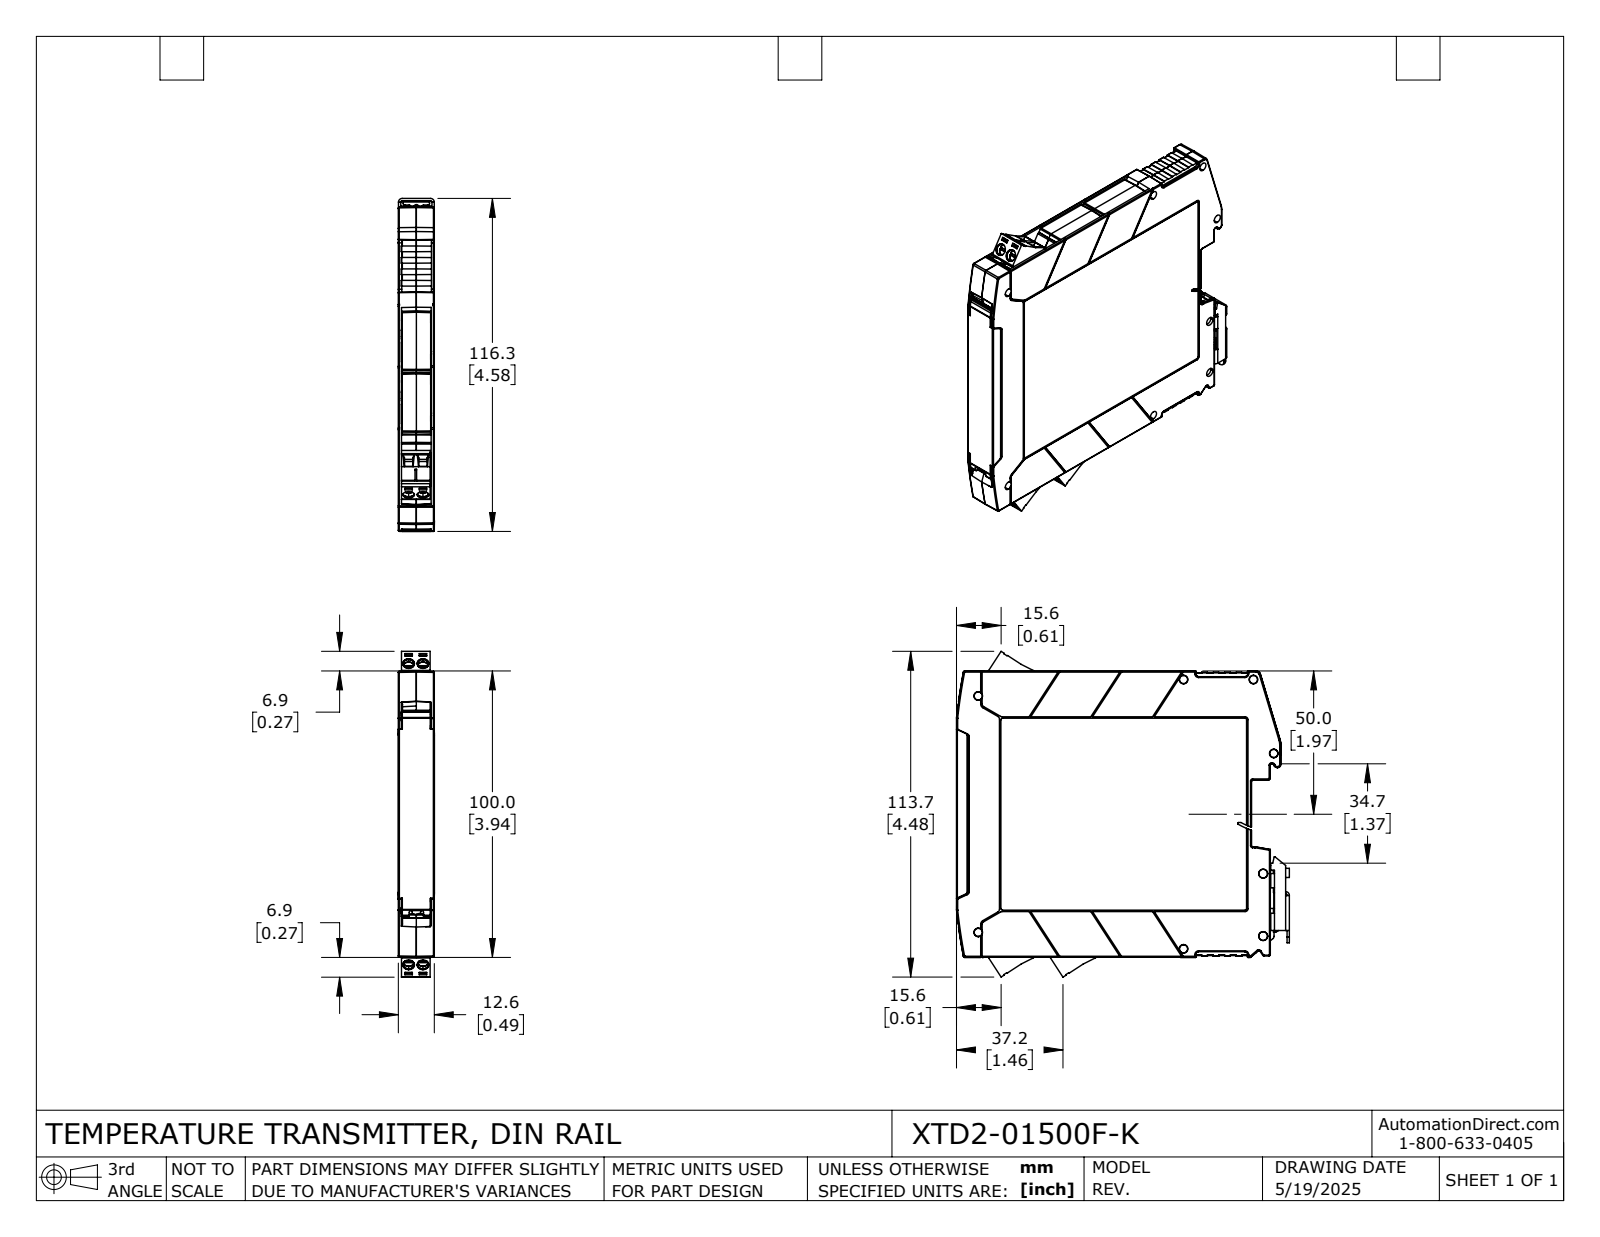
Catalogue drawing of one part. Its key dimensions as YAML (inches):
part_name: "XTD2-01500F-K"
step_written_by: "SolidWorks 2024 (AUTOMOTIVE_DESIGN)"
units: inches
bodies: {solids: 14, faces: 3337, planar: 1910, cylindrical: 596, other: 831}
overall_size: [4.577, 4.478, 0.496]
volume: 2.41
surface_area: 101.5
round_holes:
  - {diameter: 0.063, count: 6}
  - {diameter: 0.11, count: 6}
  - {diameter: 0.152, count: 6}
  - {diameter: 0.159, count: 6}
round_bosses_or_shafts:
  - {diameter: 0.156, count: 6}
  - {diameter: 0.098, count: 6}
  - {diameter: 0.059, count: 2}
  - {diameter: 0.053, count: 2}
partial_cylinders:
  - {radius: 0.008, count: 89}
  - {radius: 0.012, count: 78}
  - {radius: 0.02, count: 71}
  - {radius: 0.039, count: 22}
  - {radius: 0.004, count: 20}
  - {radius: 0.016, count: 13}
  - {radius: 0.006, count: 12}
  - {radius: 0.028, count: 8}
face_to_face_distances: [0.049, 0.445, 0.494, 0.396, 0.043, 0.451, 0.402, 0.031, 0.198, 0.247]
hole_center_spacings: [0.197, 0.464, 0.504, 0.713, 0.739]
